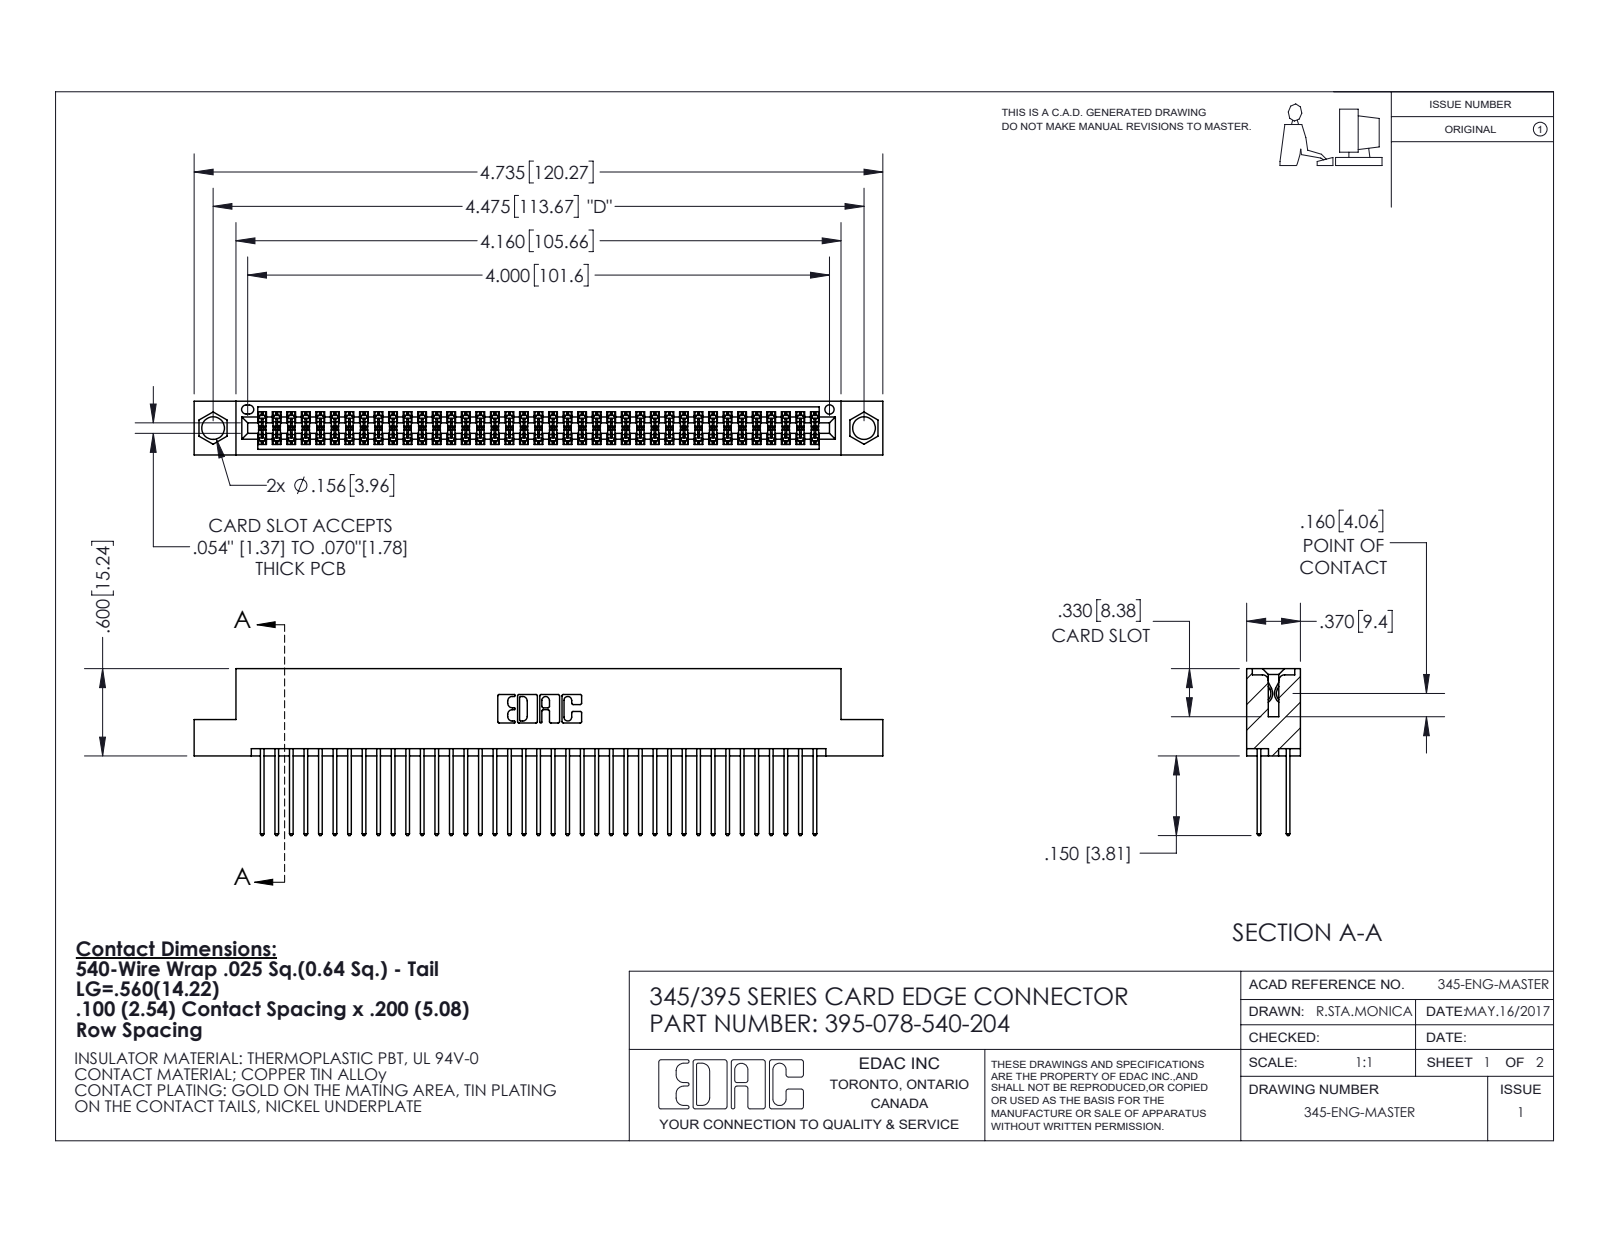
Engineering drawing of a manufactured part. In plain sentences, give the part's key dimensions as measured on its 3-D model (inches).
The part is named "345 Part_Flush Mounting Lugs - 0.156 Dia-TI; 345-292-001_345-293-140; 395-078-540-204". Its 3-D file was written by "SolidWorks 2020 (CONFIG_CONTROL_DESIGN)". It is 79 solids with 4040 faces: 2668 planar, 1372 cylindrical and 0 other. Overall it measures 4.735 by 1.147 by 0.37 inches. Its volume is 0.723 cubic inches and its surface area 28.95 square inches. Round holes: 2 of diameter 0.156, 1 of diameter 0.064. Partial cylindrical surfaces (rounded edges, fillets, slot ends): 156 of radius 0.006, 78 of radius 0.01, 22 of radius 0.01, 6 of radius 0.007, 6 of radius 0.031, 3 of radius 0.026, 2 of radius 0.014, 2 of radius 0.019. The main face-to-face distances are 0.072, 0.298, 0.2, 0.098, 0.272, 0.025, 0.37, 0.225, 0.175, 0.149. The hole center spacings are 0.27, 4.239, 4.475.
